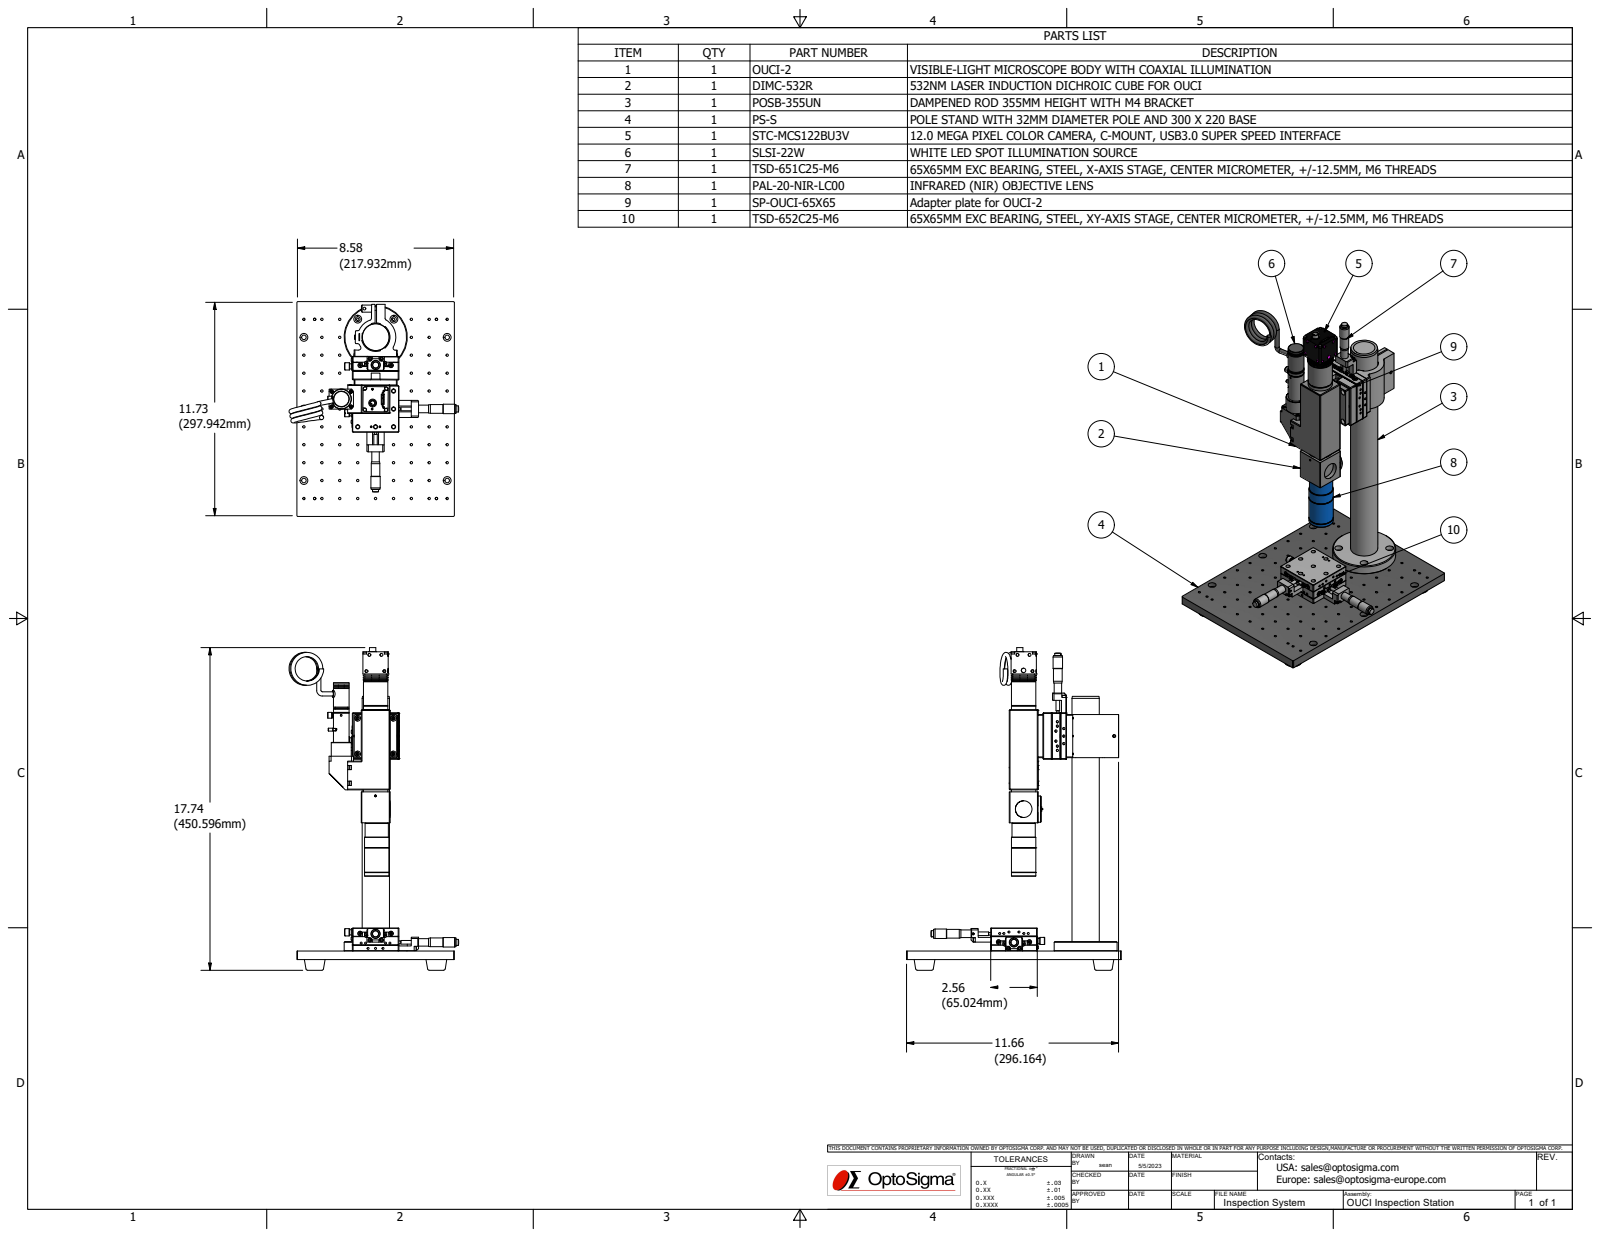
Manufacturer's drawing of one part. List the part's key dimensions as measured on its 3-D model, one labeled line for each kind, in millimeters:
Part name (STEP PRODUCT): OUCI Raman Application; OUCI-2; DIMC; POSB-355UN (+8 more)
STEP written by: Autodesk Inventor 2022 (AUTOMOTIVE_DESIGN)
Units: millimetres
Bodies: 15 solids, 3201 faces (1828 planar, 944 cylindrical, 429 other)
Overall size (bounding box): 450.48 × 300 × 236.9
Volume: 2 134 000 mm³ · Surface area: 477 012 mm²
Round holes (diameter × count): ⌀3.2 ×101, ⌀3 ×40, ⌀2.6 ×29, ⌀5 ×26, ⌀2.2 ×24, ⌀6 ×22, ⌀3.24 ×21, ⌀2 ×18, ⌀11 ×18, ⌀7 ×14, ⌀4 ×12, ⌀8 ×12
Round bosses / shafts (diameter × count): ⌀6 ×20, ⌀4.5 ×18, ⌀7 ×15, ⌀2 ×15, ⌀5.5 ×14, ⌀3 ×14, ⌀4 ×10, ⌀10 ×5
Partial cylindrical surfaces — rounded edges, fillets, slot ends (radius × count): R0.3 ×96, R3.25 ×18, R1 ×16, R3 ×12, R2 ×8, R0.1 ×6, R0.2 ×6, R2.4 ×6
Main face-to-face distances: 12, 12.5, 12.7, 7, 0.5, 40, 19.7, 20, 47, 32
Hole centre spacings: 50, 25, 55.9, 41.23, 35.36, 53.49, 6, 12
